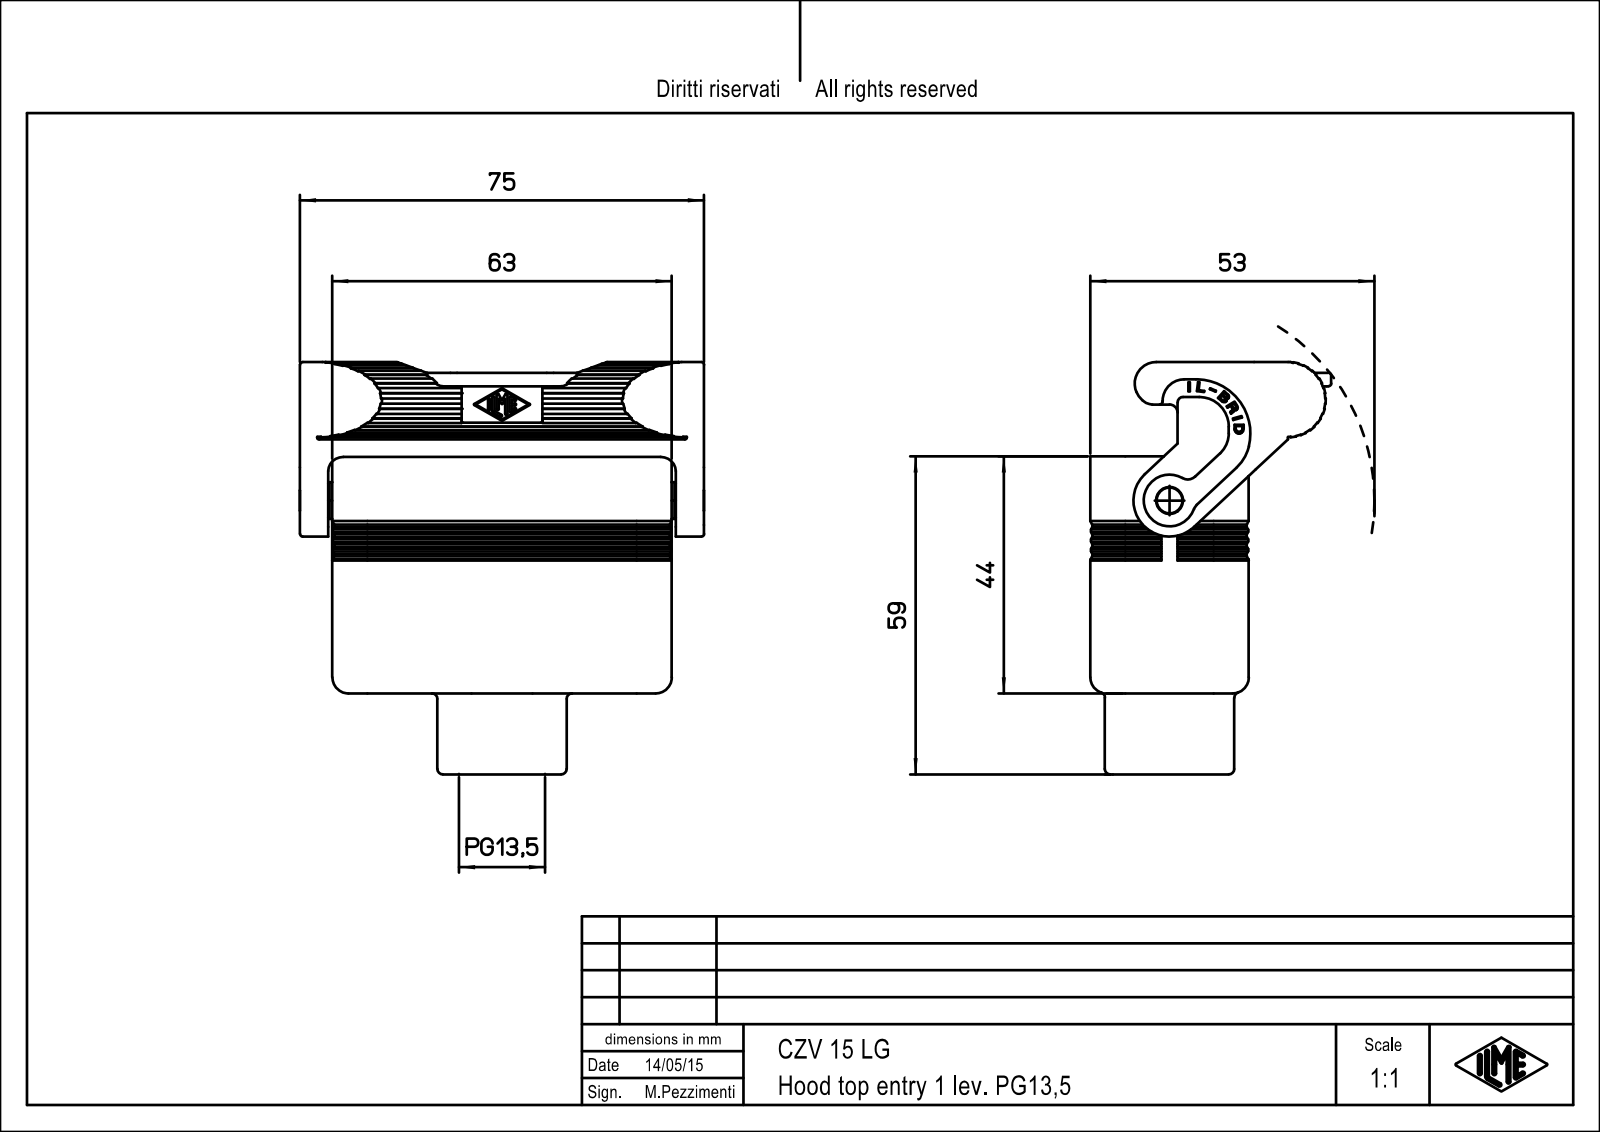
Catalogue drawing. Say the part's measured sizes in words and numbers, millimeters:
The part is named "CZV_15; LEVA_CZ15; CZV_15_LG". Its 3-D file was written by "Creo Elements/Direct Modeling 18.1F 24-Jul-2014 (C) Parametric Technology GmbH (AUTOMOTIVE_DESIGN)". It is 2 solids with 856 faces: 509 planar, 228 cylindrical and 119 other. Overall it measures 76.5 by 75.05 by 44.7 millimeters. Its volume is 41 622 cubic millimeters and its surface area 27 917 square millimeters. Round holes: 4 of diameter 3, 1 of diameter 5, 1 of diameter 16. Round bosses or shafts: 1 of diameter 24, 1 of diameter 6.8, 1 of diameter 4.8, 1 of diameter 3.2. Partial cylindrical surfaces (rounded edges, fillets, slot ends): 63 of radius 0.5, 15 of radius 0.2, 8 of radius 3.5, 7 of radius 3, 4 of radius 6.5, 3 of radius 0.1, 2 of radius 0.3, 2 of radius 2. The main face-to-face distances are 2.6, 26.8, 24.2, 29.4, 60.4, 33.2, 30.6, 6.4, 3.8, 2.5. The hole center spacings are 26.01, 16, 49.5, 52.02.
